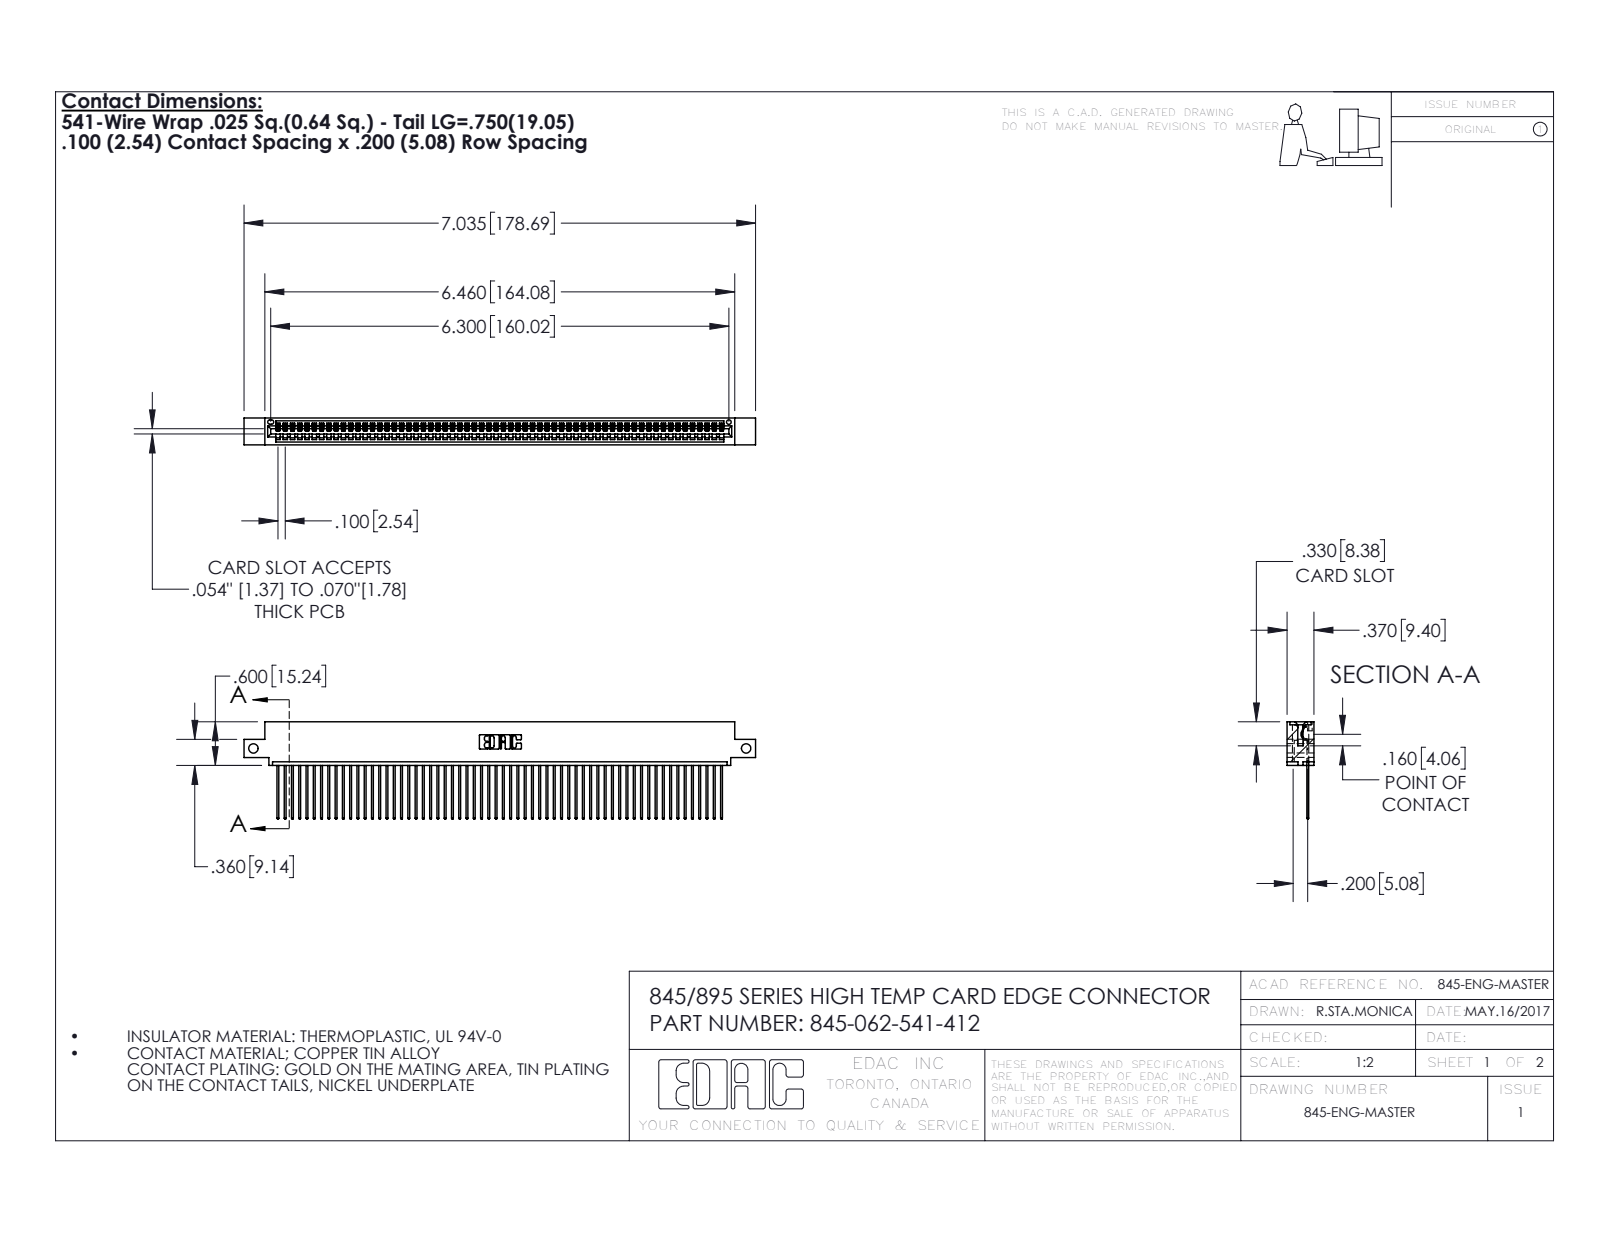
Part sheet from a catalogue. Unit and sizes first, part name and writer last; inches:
Units: inches
Overall size (bounding box): 7.035 × 1.337 × 0.37
Round holes (diameter × count): ⌀0.128 ×2, ⌀0.064 ×1
Partial cylindrical surfaces — rounded edges, fillets, slot ends (radius × count): R0.006 ×124, R0.01 ×124, R0.01 ×22, R0.007 ×6, R0.031 ×6, R0.026 ×3, R0.031 ×2, R0.04 ×2
Main face-to-face distances: 0.072, 0.298, 0.098, 0.272, 0.025, 0.37, 0.2, 0.225, 0.149, 0.072
Hole centre spacings: 6.775
Volume: 1.048 in³ · Surface area: 37.58 in²
Bodies: 63 solids, 3726 faces (2564 planar, 1162 cylindrical, 0 other)
Part name (STEP PRODUCT): 345-292-001_345-293-141; 345-062-541-412; 345 Part_0.110 Offset - Side Mount
STEP written by: SolidWorks 2016 (CONFIG_CONTROL_DESIGN)
